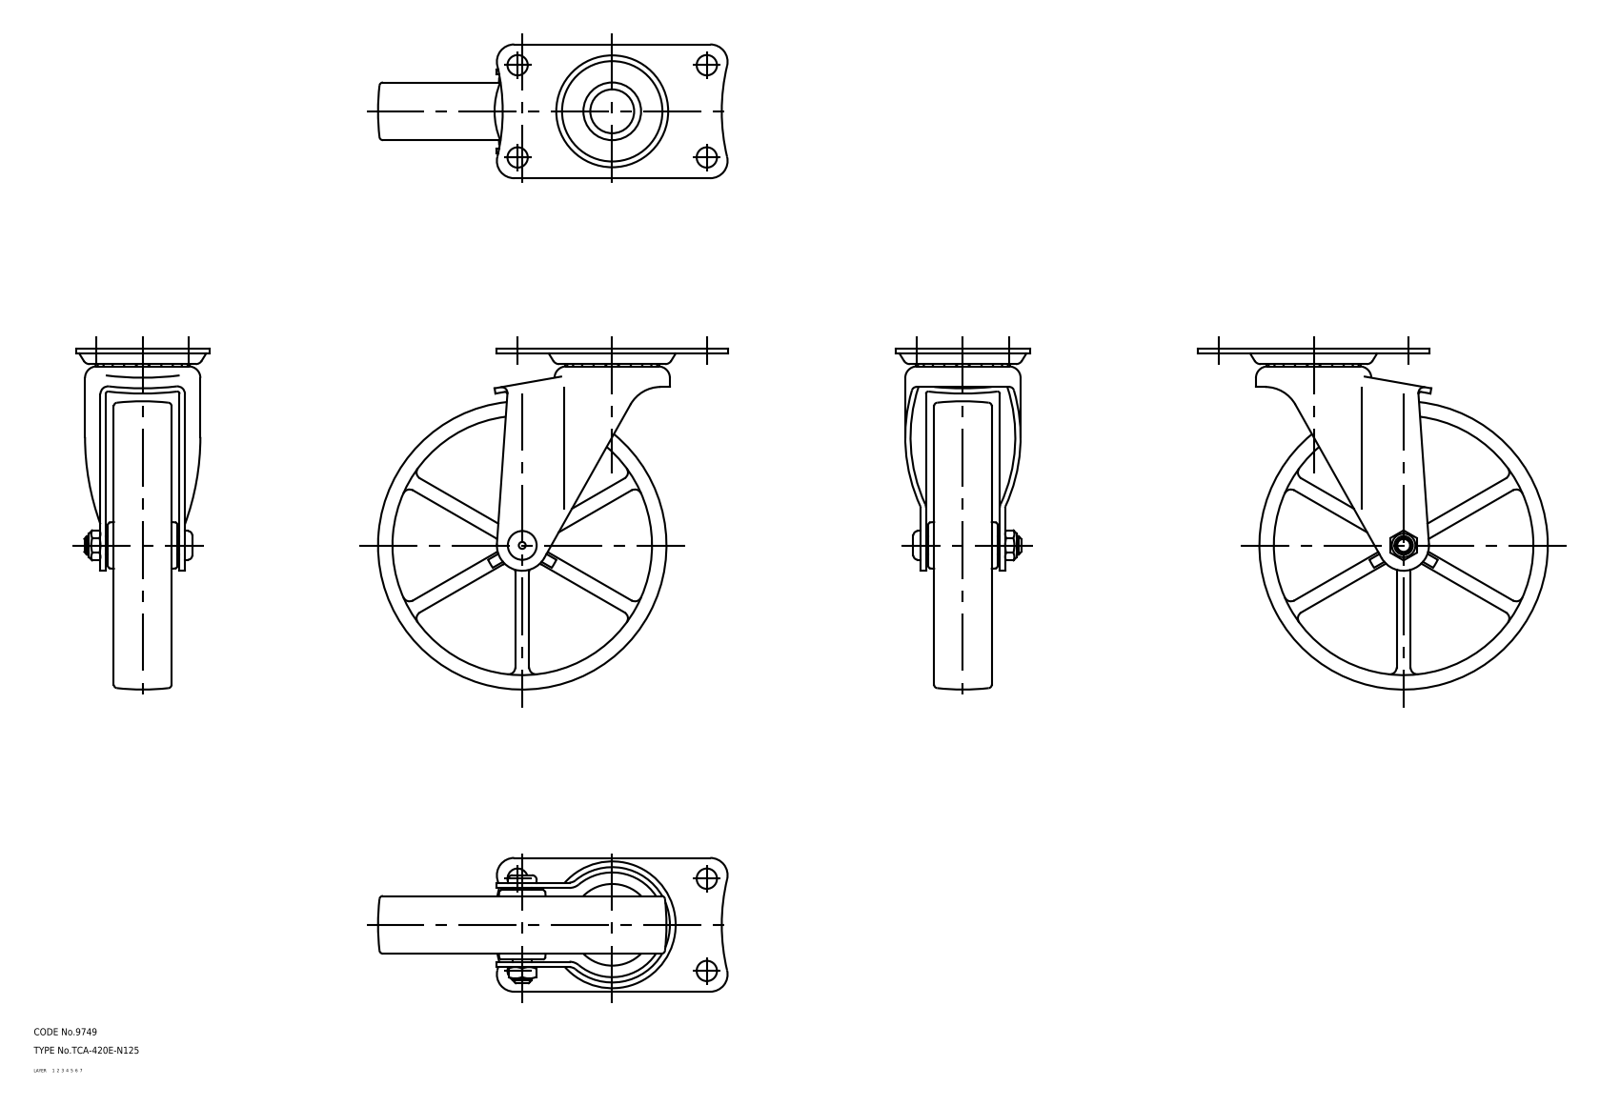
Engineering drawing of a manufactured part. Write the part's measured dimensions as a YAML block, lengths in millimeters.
part_name: "wheel; mounting plate; main shaft; axle (+1 more)"
step_written_by: "CADfix (AUTOMOTIVE_DESIGN)"
units: millimeters
bodies: {solids: 5, faces: 520, planar: 0, cylindrical: 0, other: 520}
overall_size: [151.5, 148, 58]
volume: 265595
surface_area: 77889
